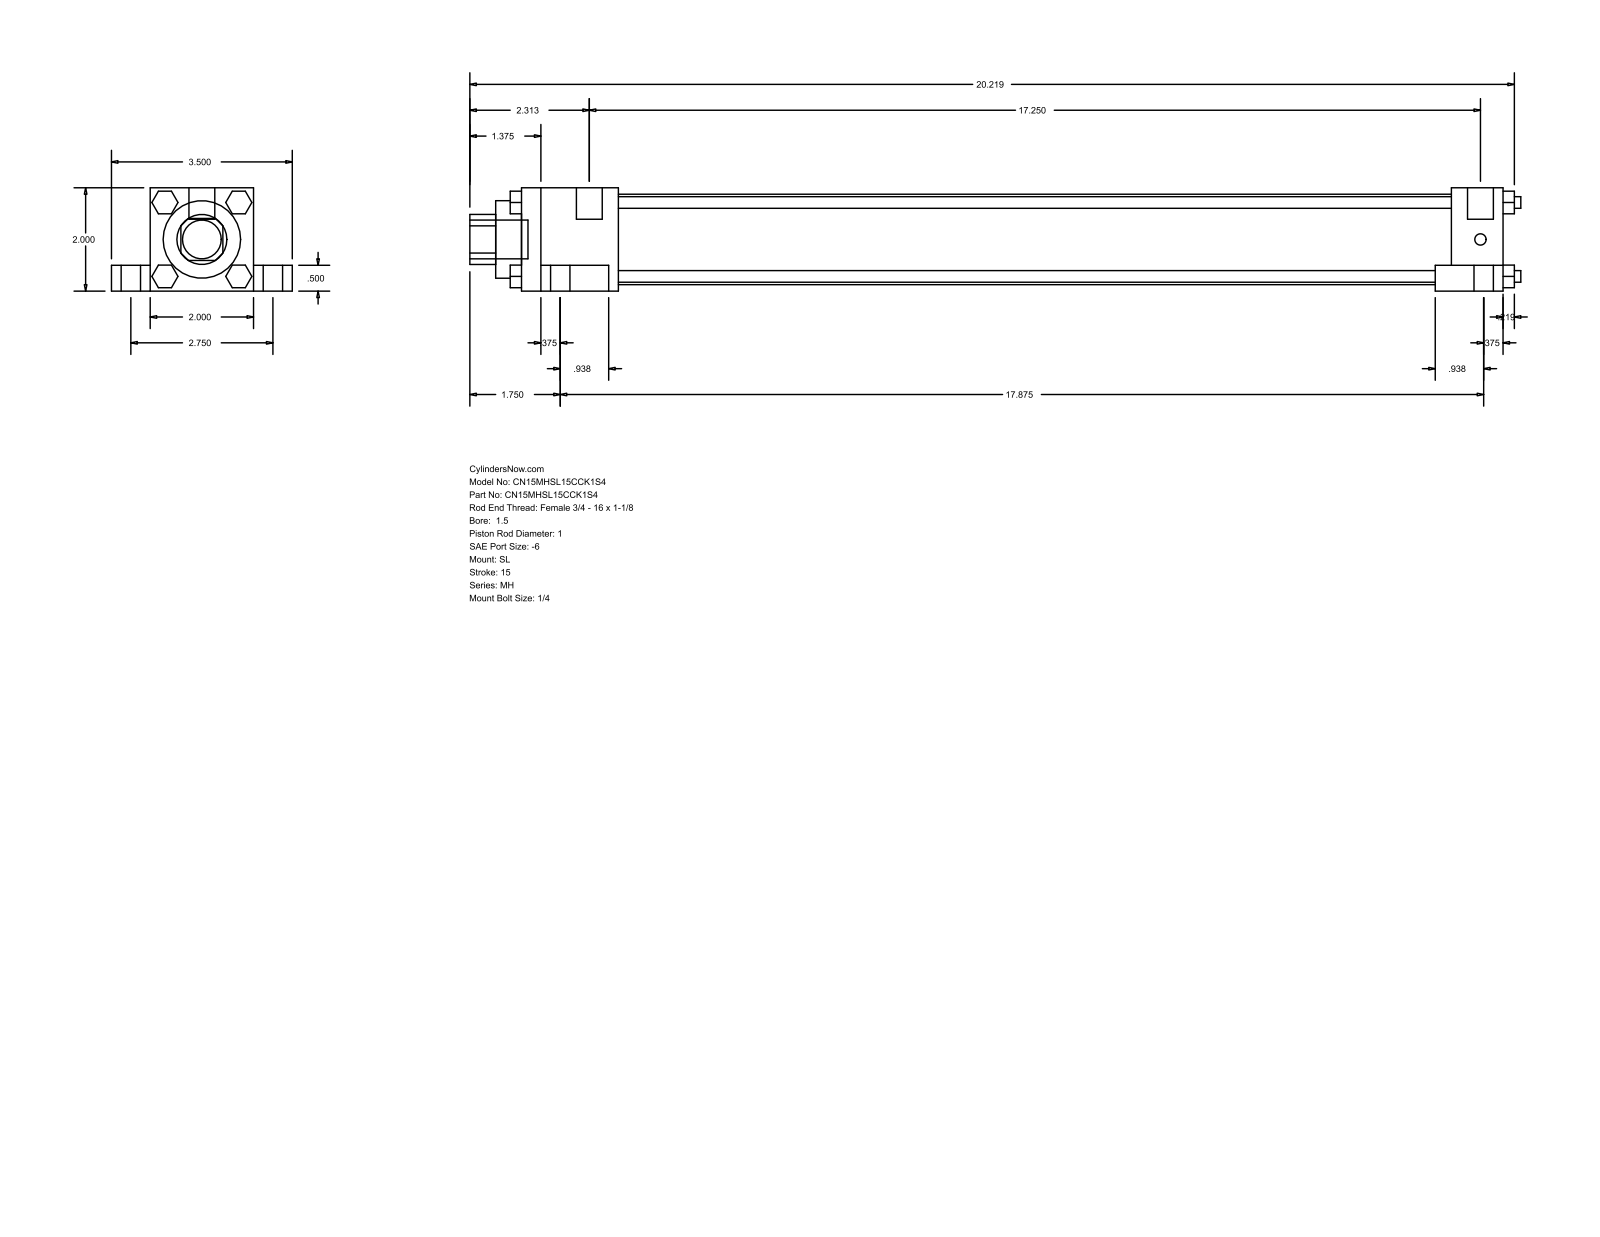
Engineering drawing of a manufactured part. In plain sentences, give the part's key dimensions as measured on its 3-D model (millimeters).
The part is named "MH_SL__0150_1". Its 3-D file was written by "GSSL Pune (CONFIG_CONTROL_DESIGN)". It is 0 solids with 148 faces: 112 planar, 36 cylindrical and 0 other. Overall it measures 516.73 by 88.9 by 50.8 millimeters. Round holes: 1 of diameter 25.4, 1 of diameter 38.1, 1 of diameter 44.45. Round bosses or shafts: 4 of diameter 15.88, 4 of diameter 9.53, 4 of diameter 5.71, 4 of diameter 5.56, 2 of diameter 12.7, 1 of diameter 19.05. Partial cylindrical surfaces (rounded edges, fillets, slot ends): 1 of radius 12.29. The main face-to-face distances are 50.8, 12.7, 38.1, 19.05, 69.85, 482.6, 25.4, 9.52, 33.34, 439.74.
